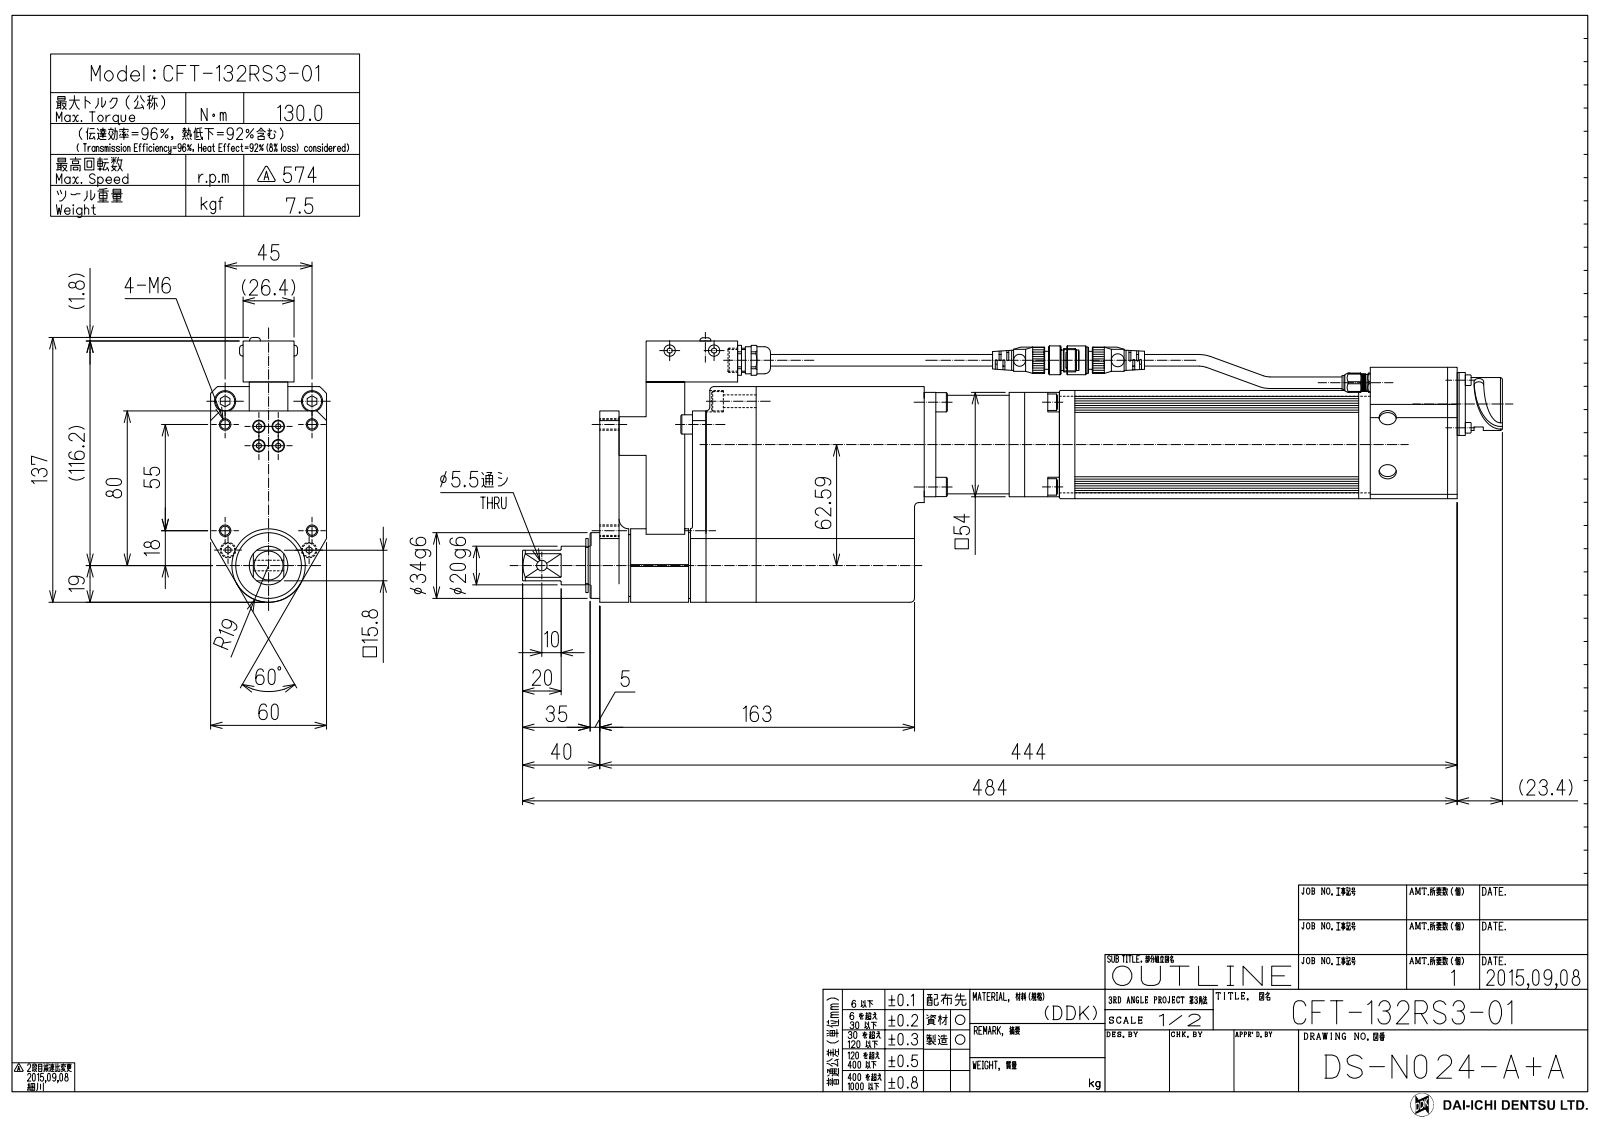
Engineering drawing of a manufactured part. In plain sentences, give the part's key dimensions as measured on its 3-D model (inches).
The part is named "CFT-132RS3-O". Its 3-D file was written by "SolidWorks 2014 (AUTOMOTIVE_DESIGN)". It is 10 solids with 343 faces: 201 planar, 96 cylindrical and 46 other. Overall it measures 19.976 by 5.388 by 2.362 inches. Its volume is 92.57 cubic inches and its surface area 304.9 square inches. Round holes: 4 of diameter 0.197, 1 of diameter 0.217, 1 of diameter 0.764. Round bosses or shafts: 4 of diameter 0.394, 4 of diameter 0.335, 3 of diameter 0.276, 1 of diameter 2.008, 1 of diameter 1.496, 1 of diameter 1.339, 1 of diameter 1.26, 1 of diameter 1.102. Partial cylindrical surfaces (rounded edges, fillets, slot ends): 4 of radius 0.039, 3 of radius 0.079, 2 of radius 0.354, 2 of radius 0.472, 1 of radius 0.965, 1 of radius 1.102. The main face-to-face distances are 0.984, 2.362, 2.756, 6.22, 7.795, 0.787, 6.614, 0.197, 3.465, 4.449. The hole center spacings are 0.979, 1.772, 2.165, 2.73, 2.798.
